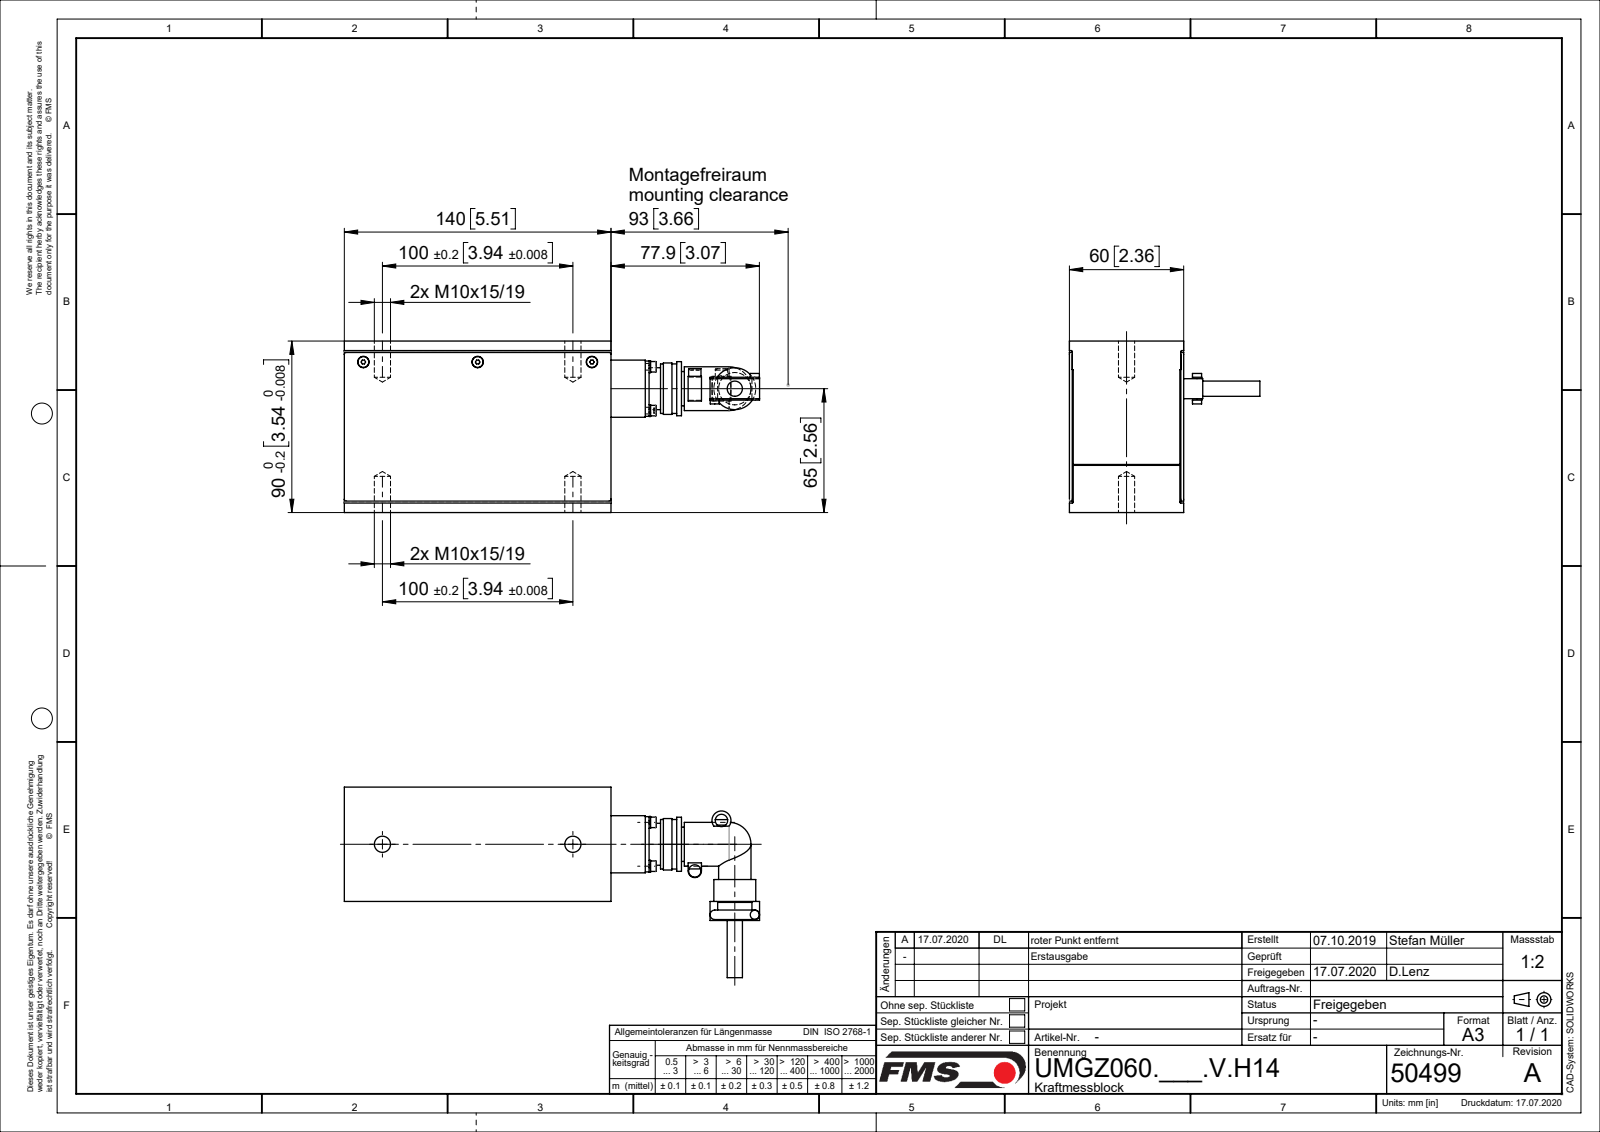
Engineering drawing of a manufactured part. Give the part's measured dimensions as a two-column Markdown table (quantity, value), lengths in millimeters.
| quantity | value |
| --- | --- |
| part name | U50499; U5124404; U49515; SENKSCHRAUBE_I-6KT_M3X6 (+6 more) |
| STEP written by | Mechanical Desktop 2009 (CONFIG_CONTROL_DESIGN) |
| units | millimeters |
| bodies | 19 solids, 417 faces (166 planar, 168 cylindrical, 83 other) |
| overall size | 218 × 100 × 90 |
| volume | 700 820 mm³ |
| surface area | 124 891 mm² |
| round holes (diameter × count) | 2.6 × 7, 3.2 × 4, 3.4 × 4, 3.5 × 4, 6 × 3, 8.68 × 2, 8.91 × 1, 23 × 1 |
| round bosses / shafts (diameter × count) | 3 × 7, 6.2 × 4, 5.5 × 4, 22 × 2, 6.5 × 2, 4.8 × 2, 28.4 × 1, 27 × 1 |
| partial cylindrical surfaces (radius × count) | 1 × 4, 9 × 4, 2.5 × 2, 3.5 × 1, 5 × 1 |
| main face-to-face distances | 1.5, 58.5, 57, 60, 10, 8.5, 50, 2, 0.5, 58 |
| hole center spacings | 16.26, 23, 32.53, 60, 100, 120 |
